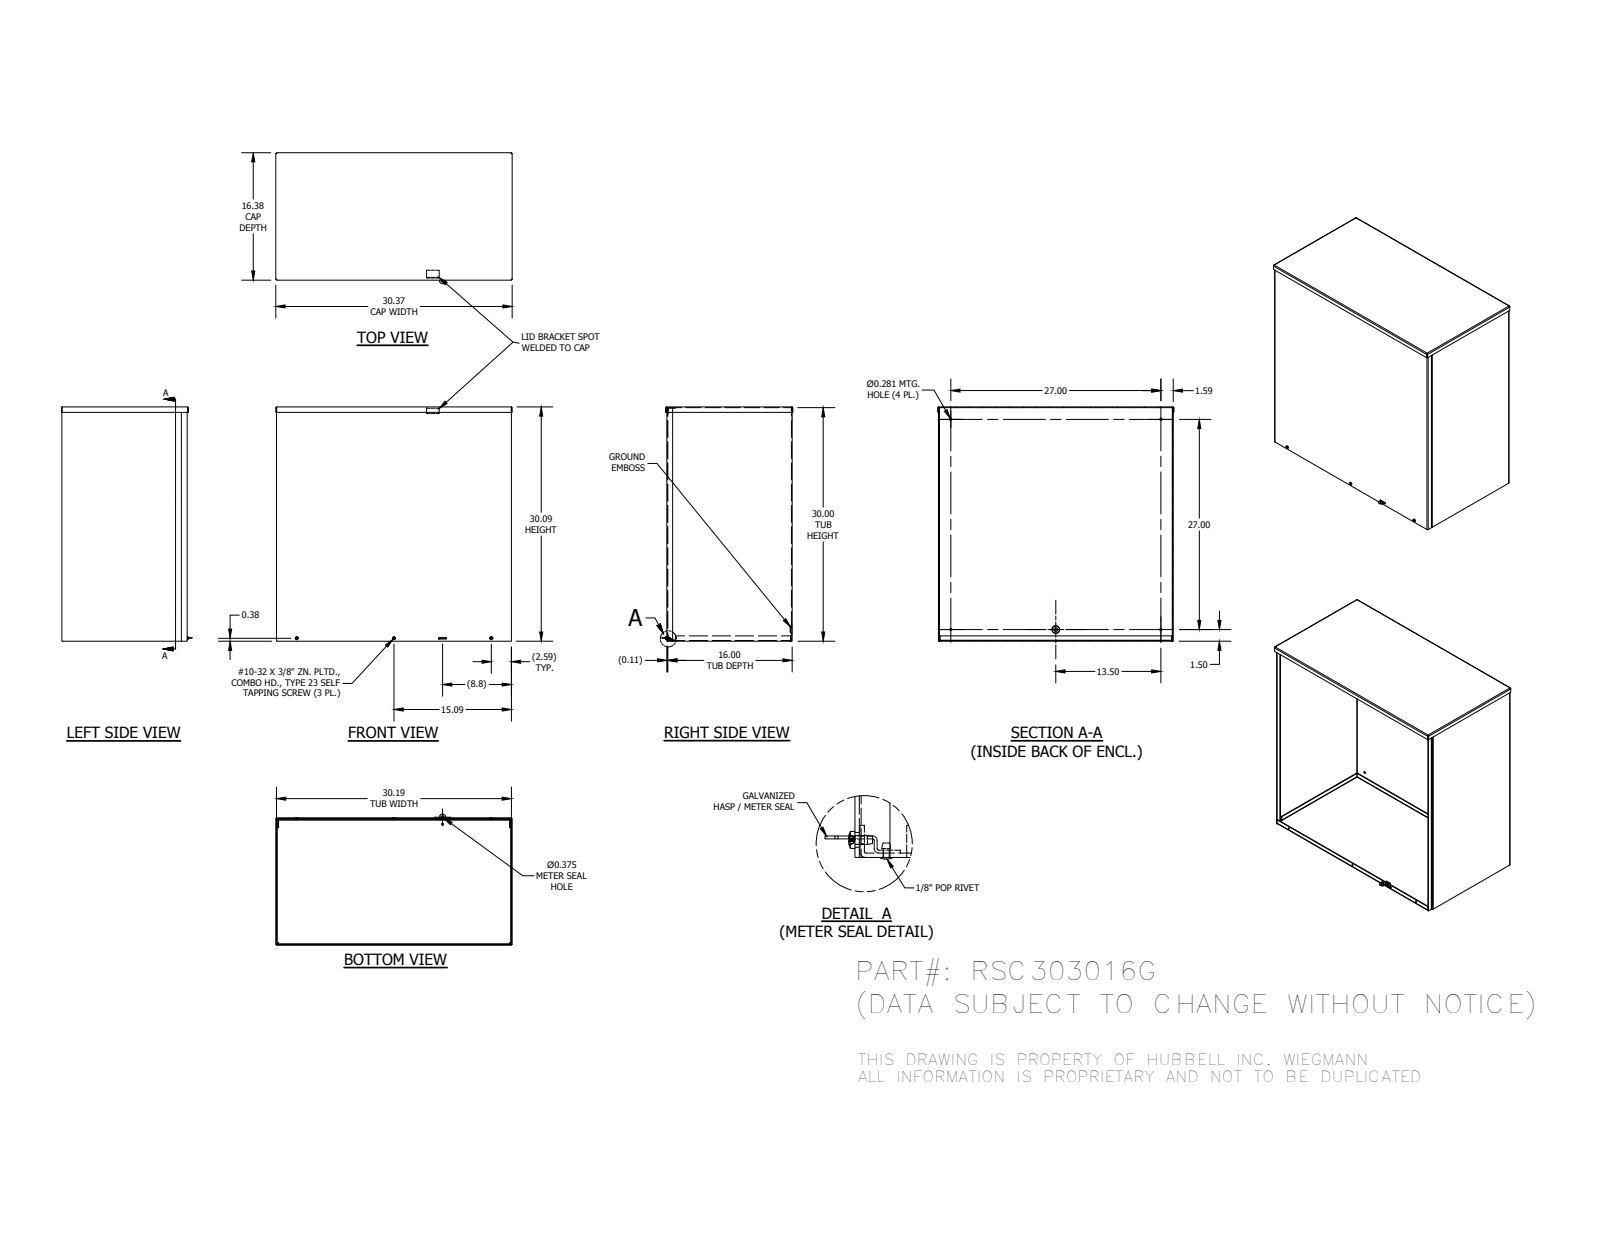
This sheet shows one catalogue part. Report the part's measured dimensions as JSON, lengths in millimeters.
{"part_name": "RSC303016GBKPA; RSC3016GEWPA; RSC3030GLFA; RSC3016GCPA (+5 more)", "step_written_by": "Autodesk Inventor 2014 (AUTOMOTIVE_DESIGN)", "units": "millimeters", "bodies": {"solids": 11, "faces": 367, "planar": 226, "cylindrical": 64, "other": 77}, "overall_size": [771.52, 765.4, 427.84], "volume_mm3": 5963000, "surface_area_mm2": 5046000, "round_holes": [[7.94, 6], [4.34, 4], [7.14, 4], [3.17, 1], [3.45, 1], [9.52, 1]], "round_bosses_or_shafts": [[4.83, 3], [6.65, 1], [3.17, 1]], "partial_cylinders_radius": [[0.79, 19], [3.17, 16], [2.37, 2], [2.67, 1], [10.16, 1]], "face_to_face_distances": [2.38, 406.8, 764.38, 762, 409.18, 404.42, 766.76, 759.62, 4.76, 760.59], "hole_center_spacings": [317.5, 344.09, 661.02, 685.8, 792.41, 807.95, 38.24, 318.78]}
